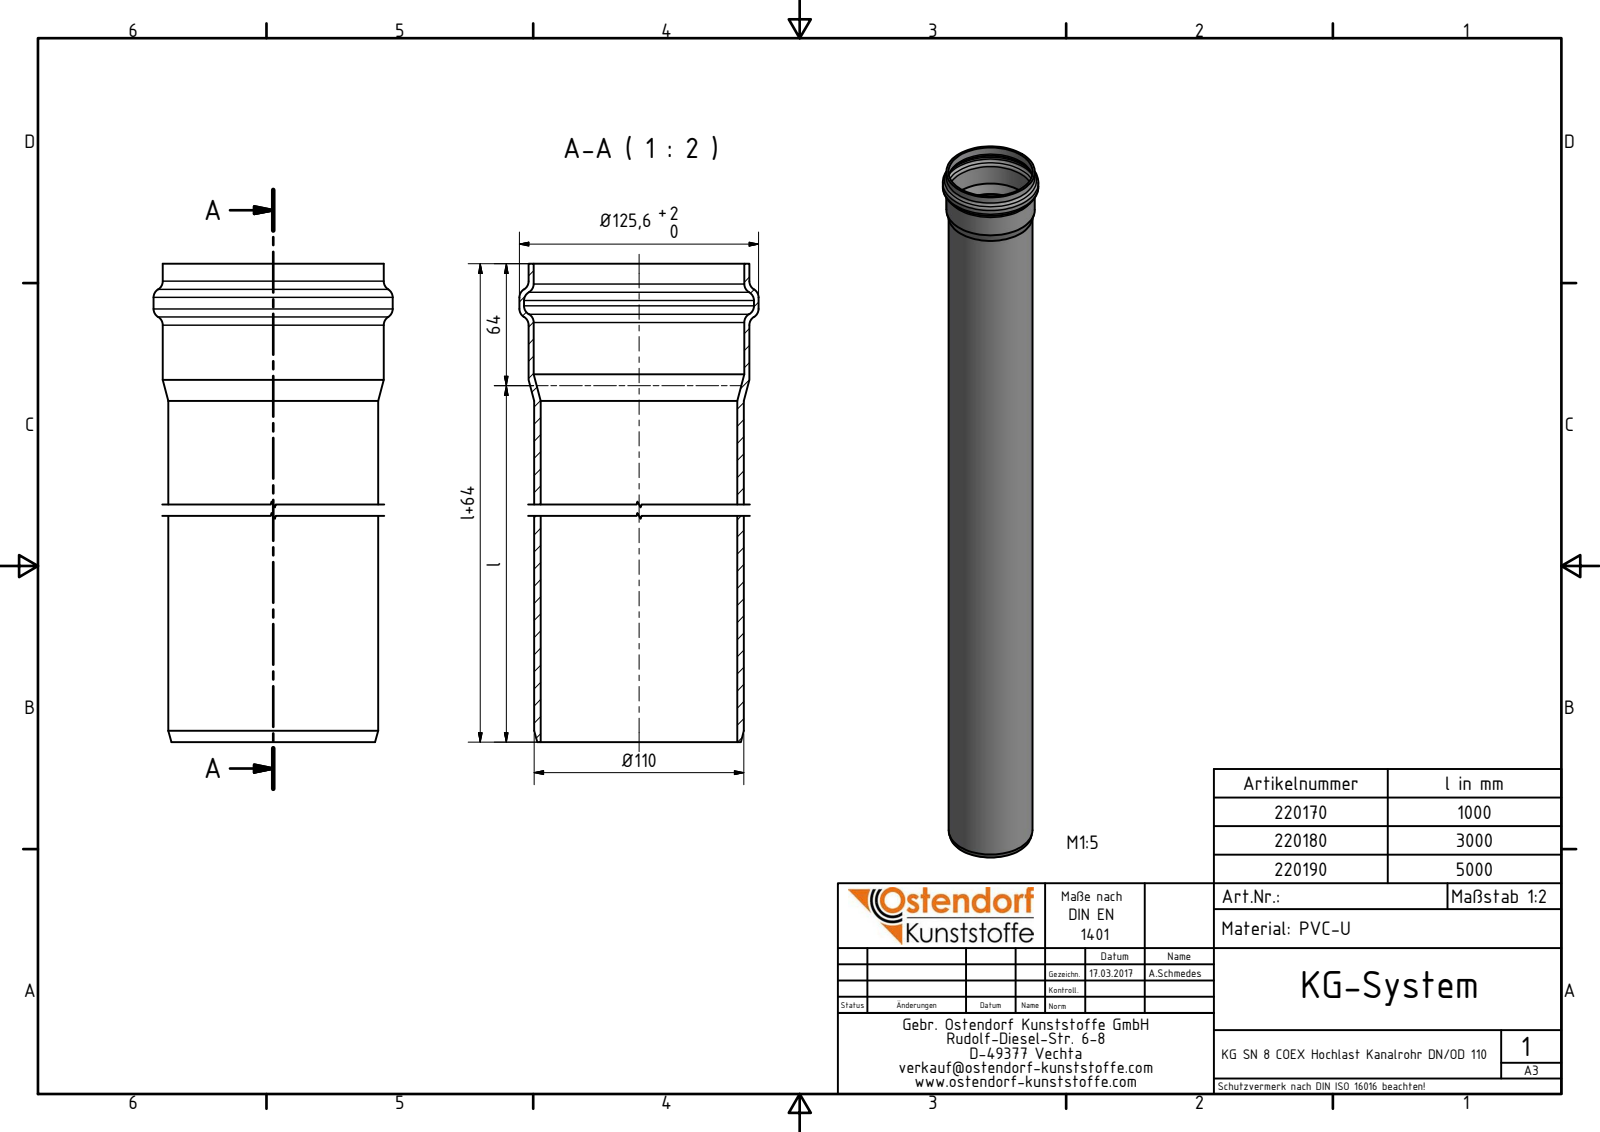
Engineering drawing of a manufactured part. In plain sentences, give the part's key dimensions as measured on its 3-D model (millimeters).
The part is named "220180 KGEM Passlängen SN 8 DN_OD 110x3000". Its 3-D file was written by "Autodesk Inventor 2016 (AUTOMOTIVE_DESIGN)". It is 1 solid with 21 faces: 2 planar, 8 cylindrical and 11 other. Overall it measures 3064 by 125.6 by 125.6 millimeters. Its volume is 3 585 000 cubic millimeters and its surface area 2 061 000 square millimeters. Round holes: 1 of diameter 103.15, 1 of diameter 110.65, 1 of diameter 120.8. Round bosses or shafts: 1 of diameter 125.6, 1 of diameter 116.05, 1 of diameter 110.15. The main face-to-face distances are 3064.
